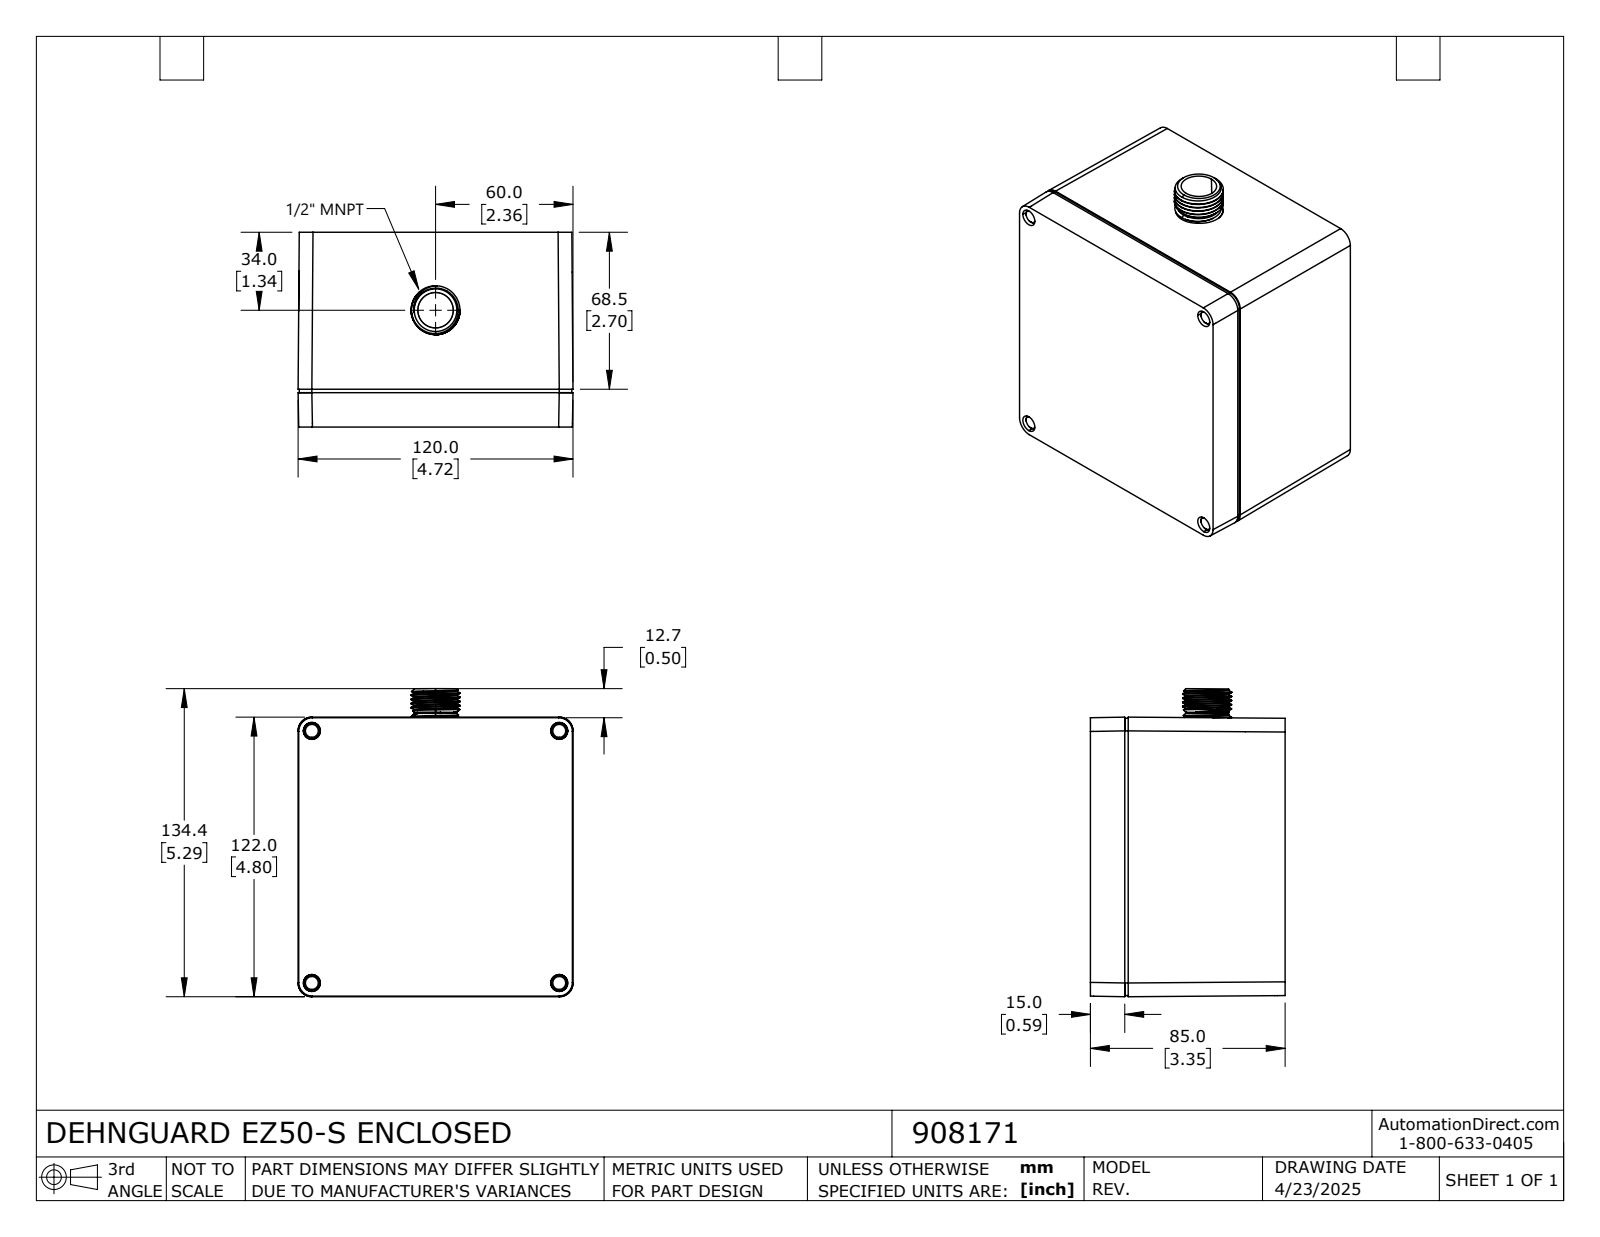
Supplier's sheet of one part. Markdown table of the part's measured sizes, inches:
| quantity | value |
| --- | --- |
| part name | 908171 |
| STEP written by | SolidWorks 2024 (AUTOMOTIVE_DESIGN) |
| units | inches |
| bodies | 2 solids, 437 faces (278 planar, 113 cylindrical, 46 other) |
| overall size | 5.293 × 4.724 × 3.346 |
| volume | 21.69 in³ |
| surface area | 267.7 in² |
| round holes (diameter × count) | 0.165 × 4, 0.315 × 4 |
| round bosses / shafts (diameter × count) | 0.276 × 6, 0.113 × 4, 1.166 × 1, 1.125 × 1, 1.026 × 1, 0.84 × 1 |
| partial cylindrical surfaces (radius × count) | 0.236 × 8, 0.217 × 4, 0.02 × 2, 0.079 × 2, 0.079 × 2, 3.937 × 2, 6.448 × 2, 6.449 × 2 |
| main face-to-face distances | 0.118, 0.157, 3.346, 3.189, 3.228, 3.071, 0.12, 0.039, 0.37, 0.119 |
| hole center spacings | 3.543, 4.331, 5.596 |
